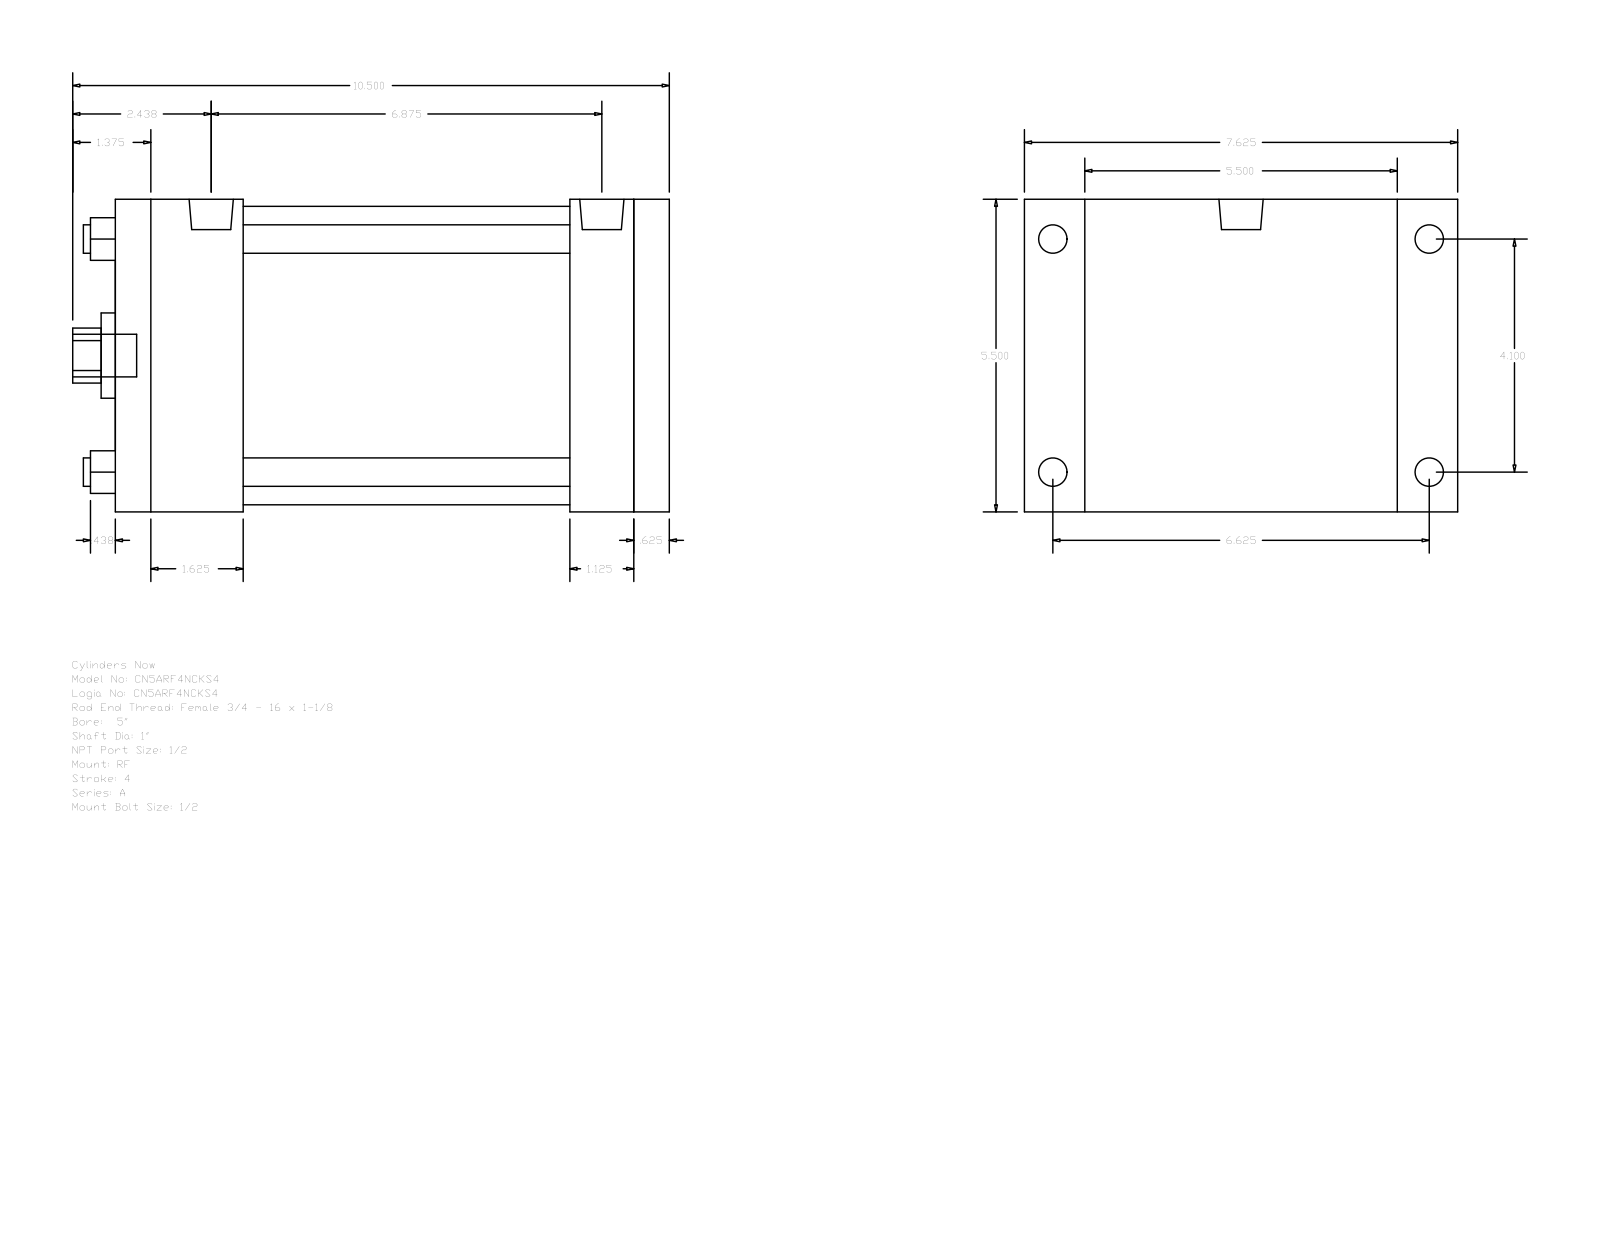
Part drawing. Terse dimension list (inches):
name: A_RF__0500_1
written by: GSSL Pune (CONFIG_CONTROL_DESIGN)
unit: in
bodies: 0 solids, 92 faces (64 planar, 28 cylindrical, 0 other)
size: 10.5 × 7.625 × 5.5
holes: 4× ⌀0.5, 1× ⌀1, 1× ⌀1.5, 1× ⌀5.25
bosses: 4× ⌀0.5, 4× ⌀0.344, 2× ⌀0.778, 1× ⌀0.75
rounds: 1× R0.484
face distances: 5.5, 9.75, 9.125, 0.625, 1.125, 2.25, 6.875, 7.5, 8, 5.75
hole spacings: 2.899, 4.1, 5.798
